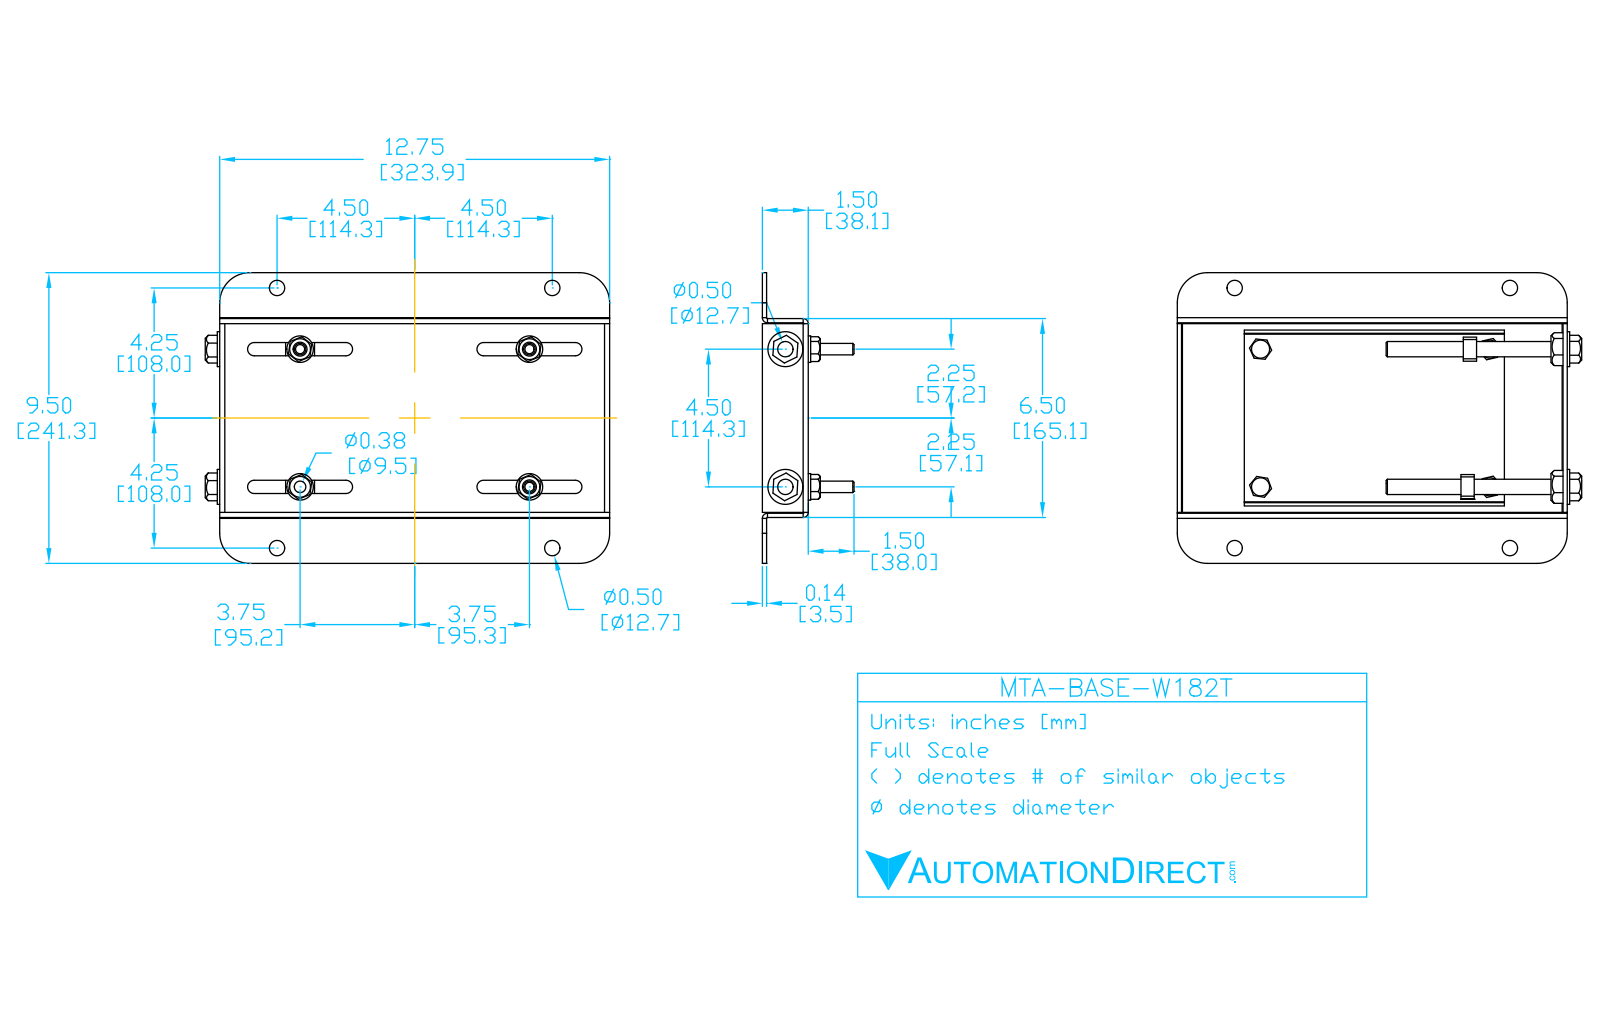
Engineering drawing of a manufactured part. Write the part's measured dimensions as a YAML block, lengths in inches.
part_name: "W182T"
step_written_by: "SolidWorks 2017 (AUTOMOTIVE_DESIGN)"
units: inches
bodies: {solids: 22, faces: 354, planar: 174, cylindrical: 112, other: 68}
overall_size: [13.222, 9.5, 3.006]
volume: 33.82
surface_area: 519.4
round_holes:
  - {diameter: 0.5, count: 6}
  - {diameter: 0.375, count: 4}
  - {diameter: 0.378, count: 4}
  - {diameter: 0.531, count: 2}
  - {diameter: 0.63, count: 2}
round_bosses_or_shafts:
  - {diameter: 0.866, count: 4}
  - {diameter: 1.142, count: 2}
  - {diameter: 0.375, count: 2}
partial_cylinders:
  - {radius: 0.029, count: 8}
  - {radius: 0.079, count: 8}
  - {radius: 0.217, count: 8}
  - {radius: 0.167, count: 6}
  - {radius: 0.984, count: 4}
  - {radius: 0.135, count: 2}
face_to_face_distances: [0.138, 1.362, 0.106, 0.244, 1.5, 1.256, 1.224, 1.118, 6.362, 12.612]
hole_center_spacings: [4.5, 7.5, 8.5, 8.746, 9, 12.38, 2.139, 2.14]
